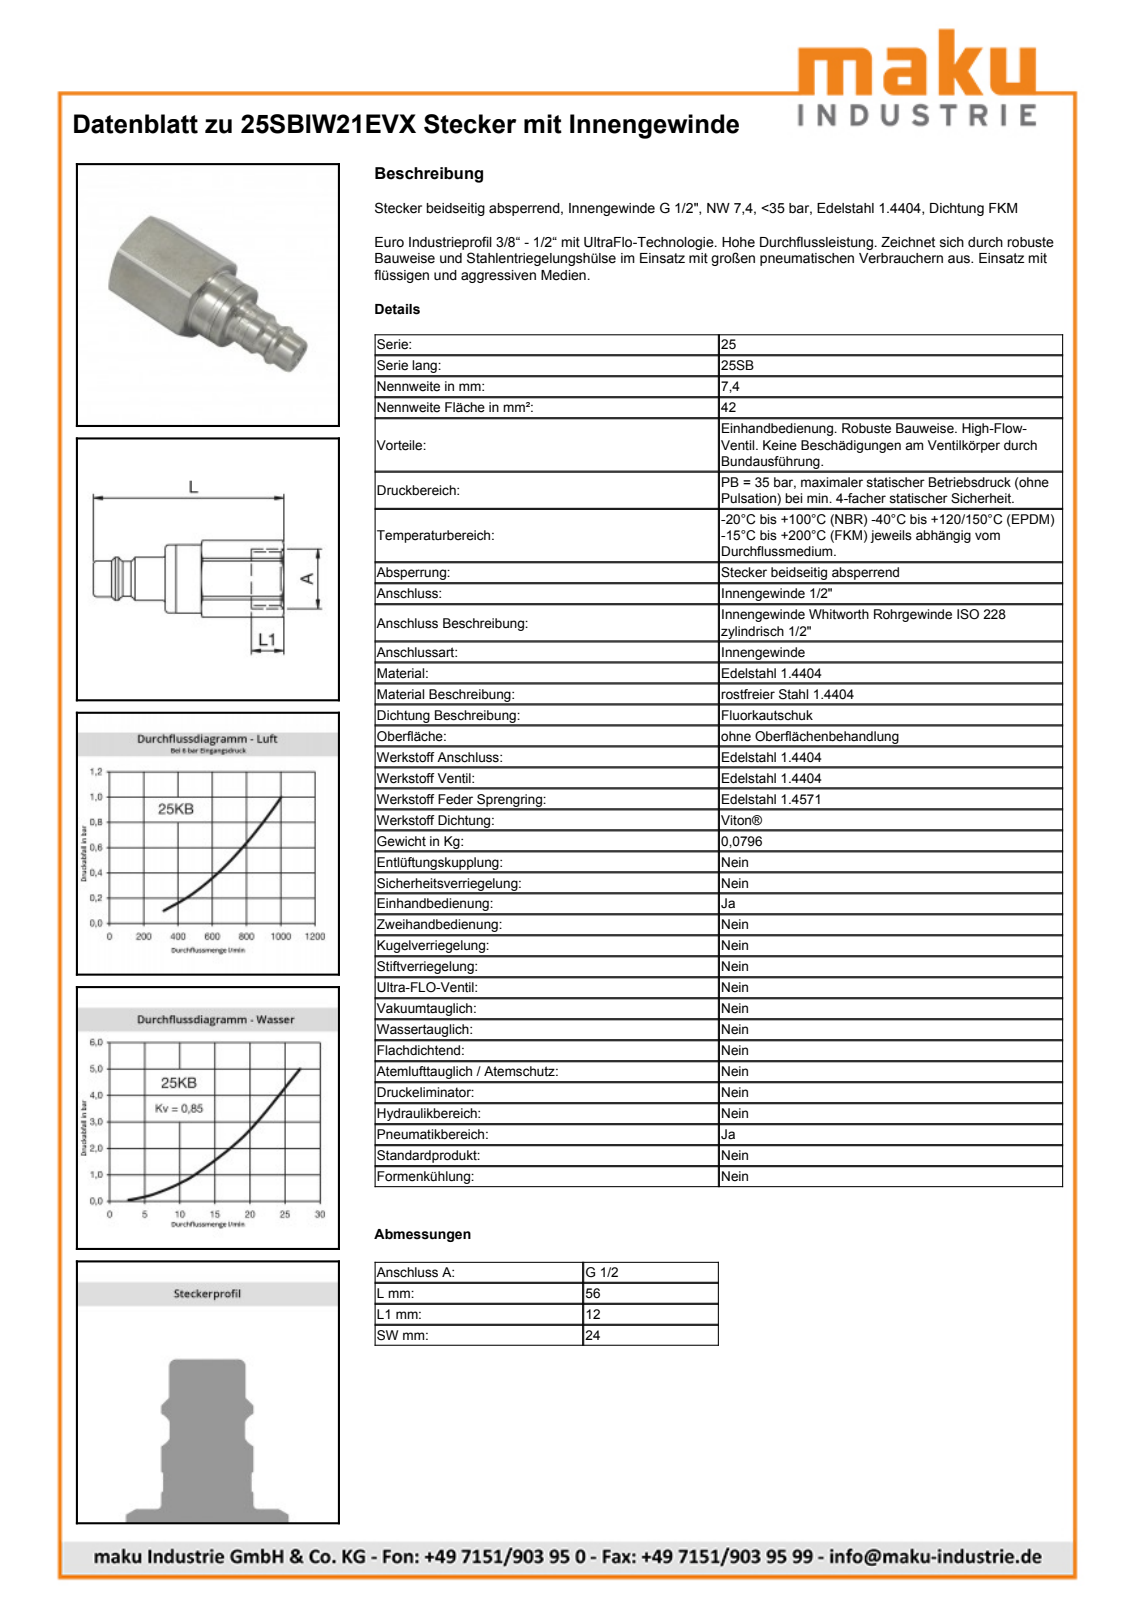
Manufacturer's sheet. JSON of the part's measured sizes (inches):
{"part_name": "D110481", "step_written_by": "Autodesk Inventor 2013 (AUTOMOTIVE_DESIGN)", "units": "inches", "bodies": {"solids": 1, "faces": 57, "planar": 16, "cylindrical": 18, "other": 23}, "overall_size": [2.205, 1.059, 1.006], "volume_in3": 0.871, "surface_area_in2": 8.581, "round_holes": [[0.551, 1], [0.63, 1], [0.733, 1]], "round_bosses_or_shafts": [[0.748, 1], [0.746, 1], [0.609, 1], [0.571, 1], [0.472, 1], [0.39, 1], [0.384, 1]], "partial_cylinders_radius": [[0.533, 1]], "face_to_face_distances": [0.944, 0.945, 0.553, 0.553, 1.026, 0.473, 0.472, 0.392, 0.944, 1.417]}
